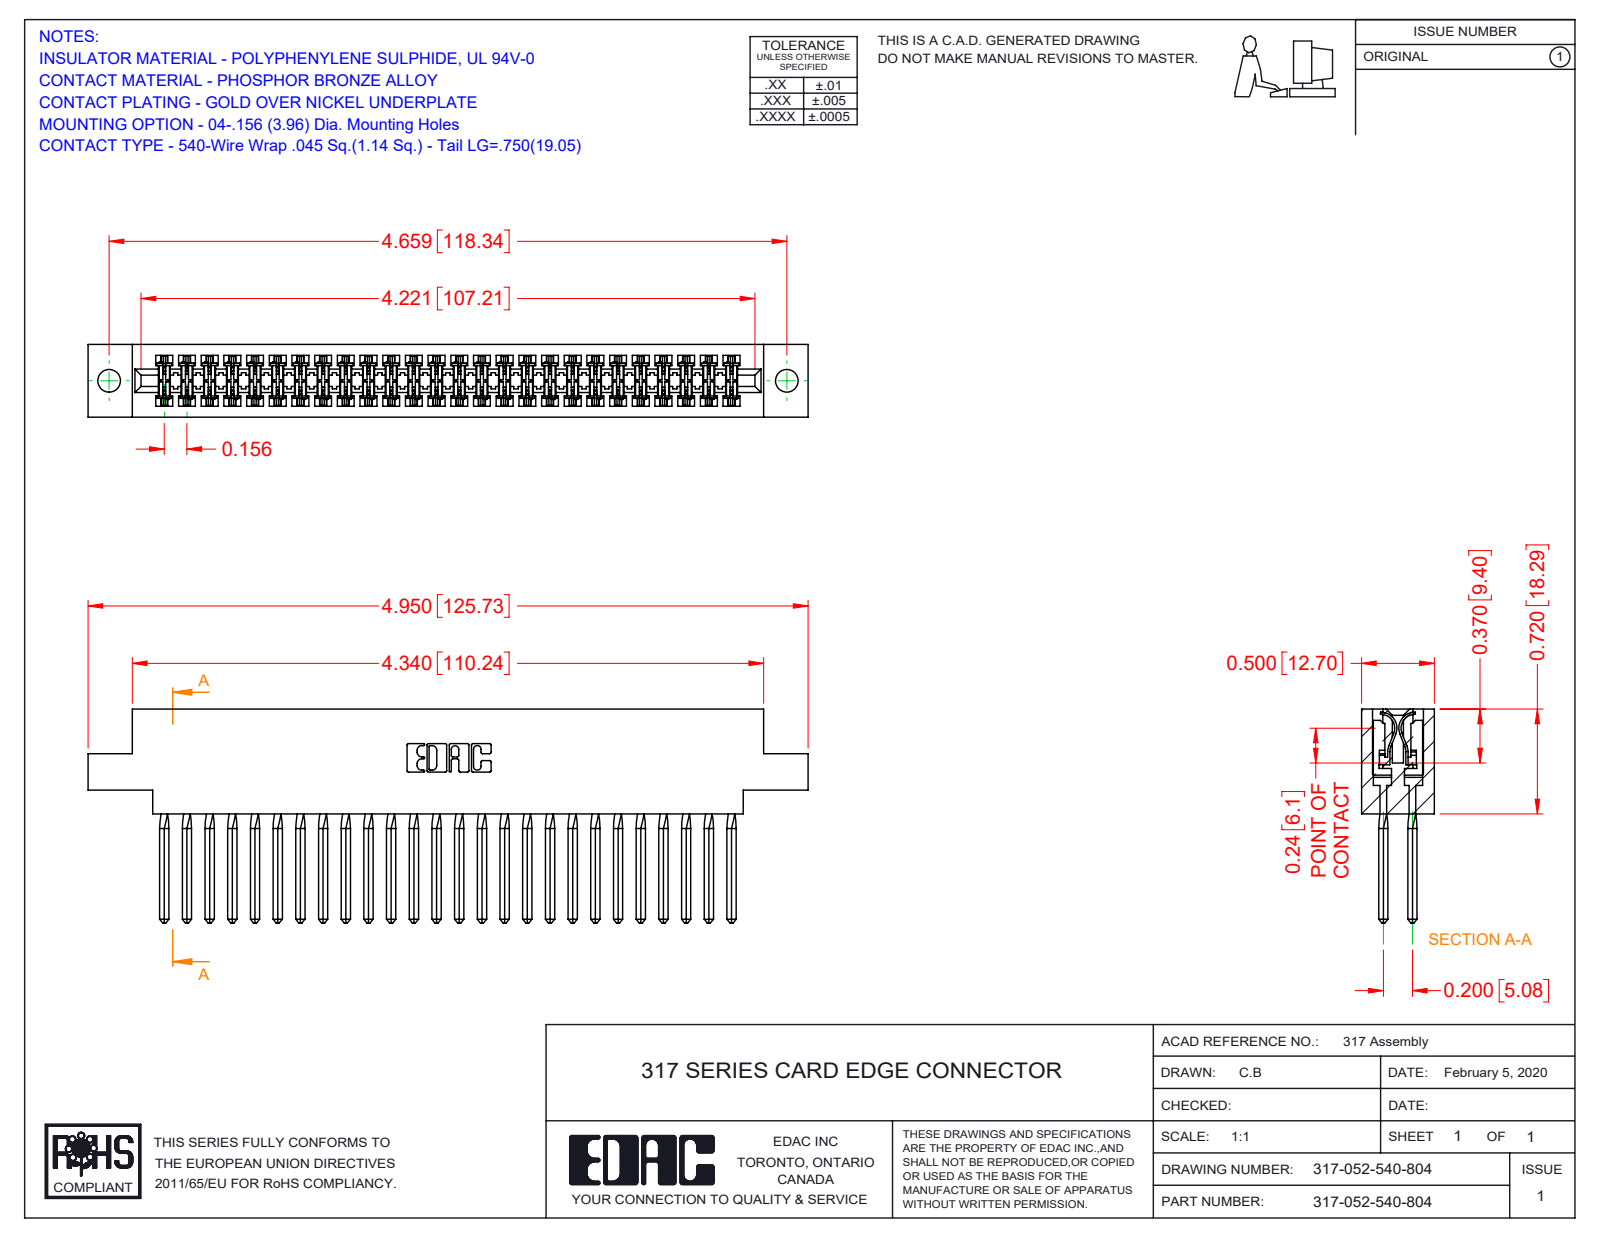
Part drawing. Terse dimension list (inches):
name: 317-052-540-804; 317 Part_.156 Dia - TH; 317-290-001_540
written by: SolidWorks 2016 (CONFIG_CONTROL_DESIGN)
unit: in
bodies: 53 solids, 4730 faces (3854 planar, 668 cylindrical, 208 other)
size: 4.95 × 1.47 × 0.5
volume: 1.249 in³; area: 46.1 in²
holes: 2× ⌀0.156
rounds: 104× R0.015, 22× R0.01, 6× R0.007, 6× R0.031, 3× R0.026, 2× R0.095, 2× R0.1, 2× R0.11
face distances: 0.5, 0.075, 0.425, 0.35, 0.11, 0.195, 0.094, 0.72, 0.2, 0.115
hole spacings: 4.659
